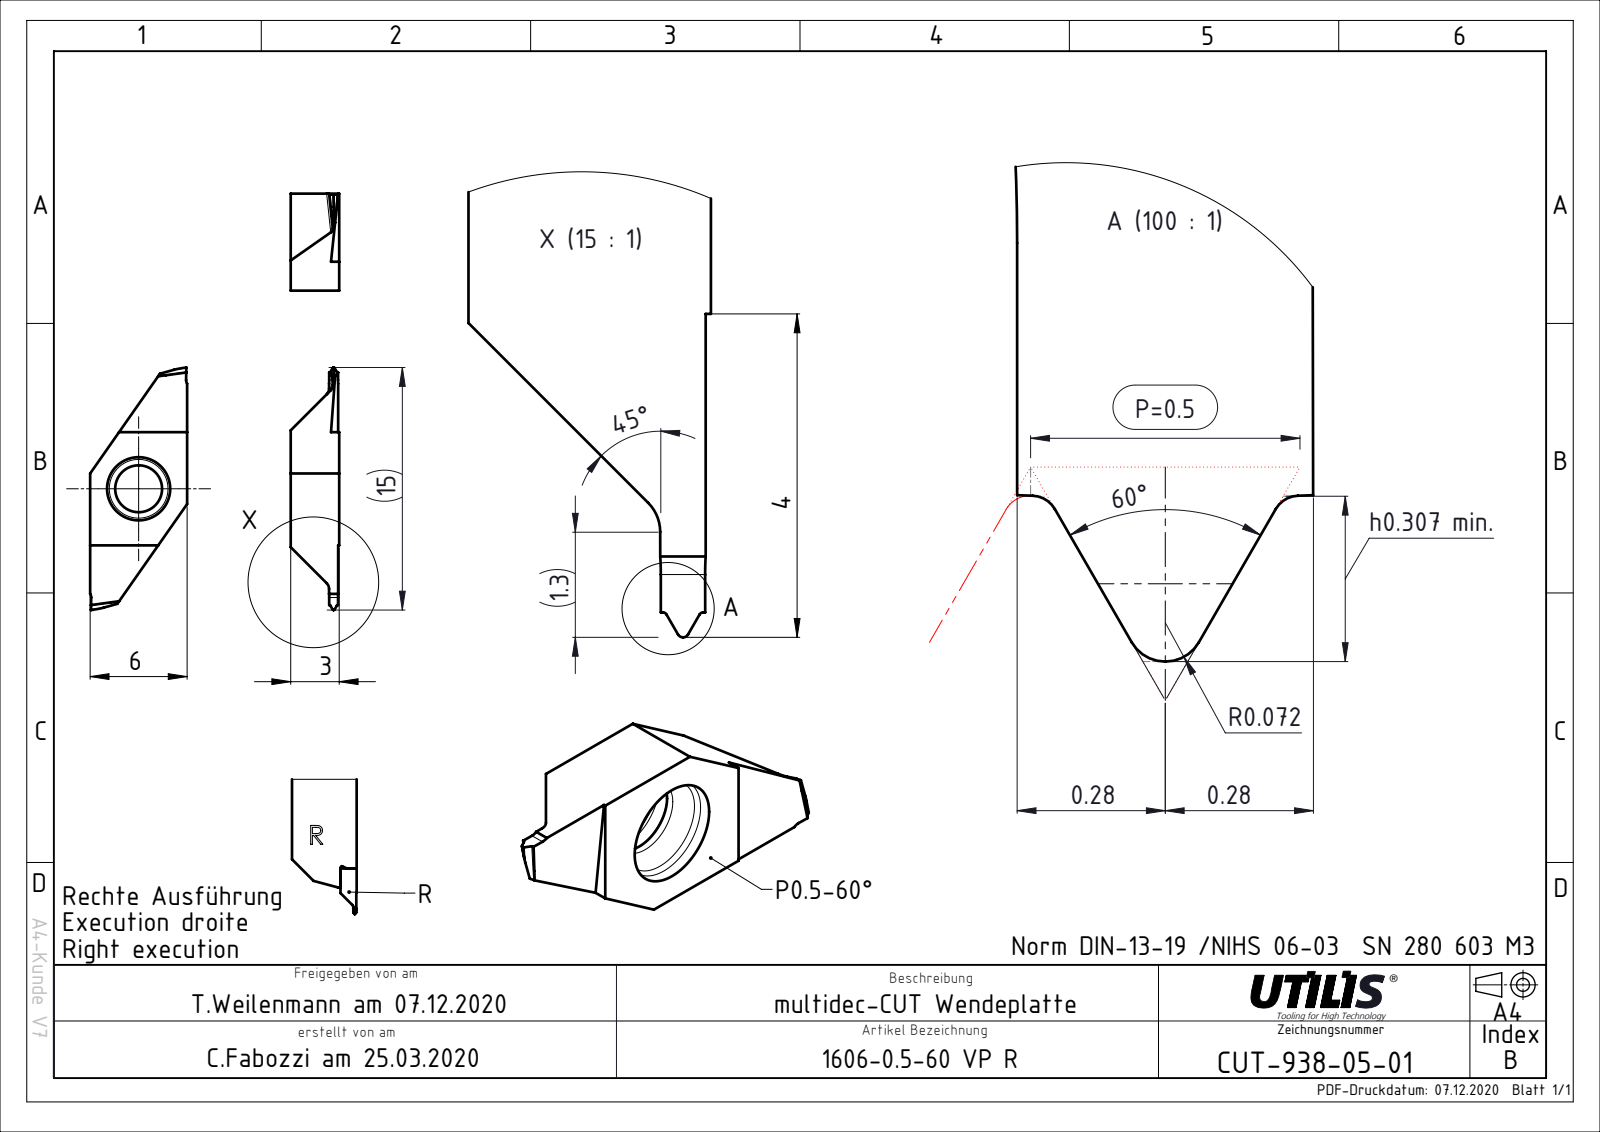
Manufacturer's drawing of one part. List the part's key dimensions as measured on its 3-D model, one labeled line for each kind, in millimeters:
Part name (STEP PRODUCT): CUT-938-05; ASME Y14.5
STEP written by: FormatWorks Professional (AP242_MANAGED_MODEL_BASED_3D_ENGINEERING_MIM_LF)
Units: millimetres
Bodies: 1 solid, 42 faces (24 planar, 14 cylindrical, 4 other)
Overall size (bounding box): 15 × 6 × 3
Volume: 126 mm³ · Surface area: 210 mm²
Round holes (diameter × count): ⌀2.9 ×1
Partial cylindrical surfaces — rounded edges, fillets, slot ends (radius × count): R0.5 ×2
Main face-to-face distances: 6, 3, 0.4, 9, 11.18, 12, 7, 12.92, 12.91
